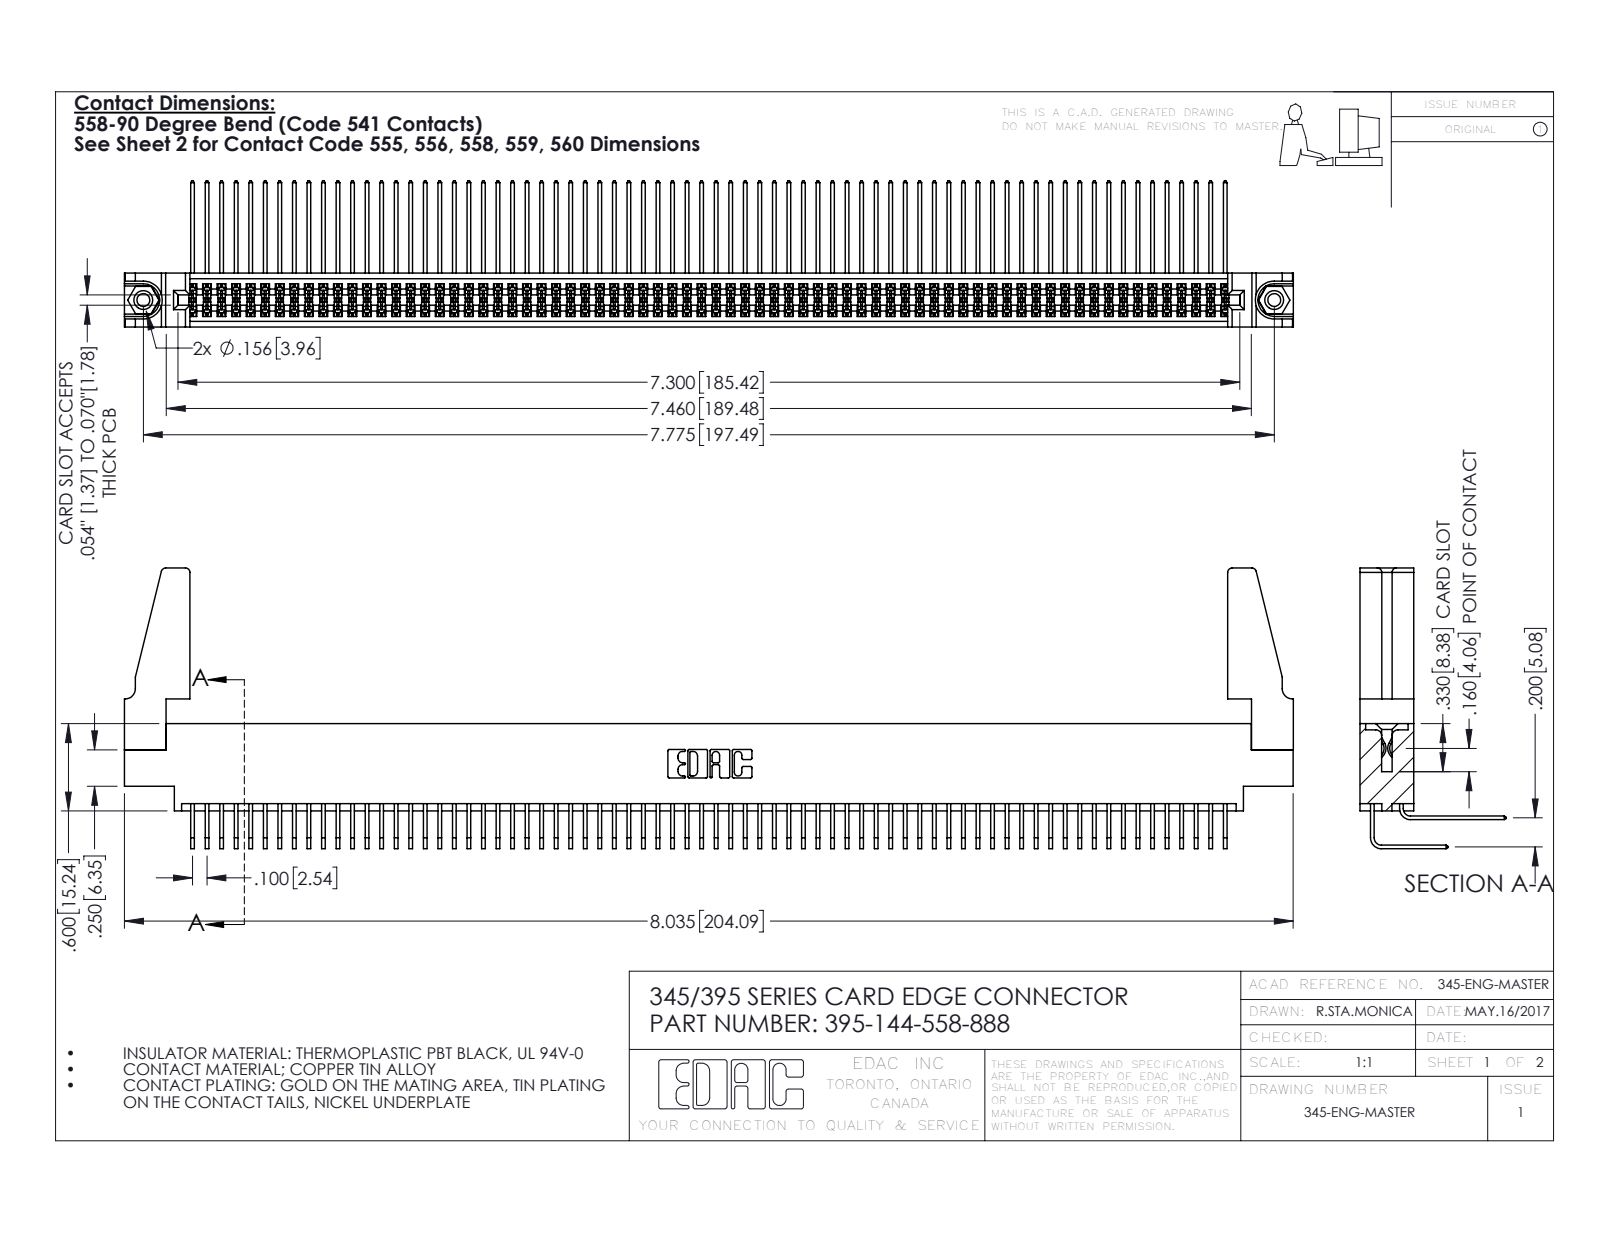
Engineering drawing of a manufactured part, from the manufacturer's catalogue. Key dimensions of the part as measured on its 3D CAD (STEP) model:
Part name (STEP PRODUCT): 345-220-078_345-220-088; 395-144-558-888; 345-292-001_558 Tail - 2; 345 Part_0.170 Offset - 0.156 Dia-TH (+2 more)
STEP written by: SolidWorks 2016 (CONFIG_CONTROL_DESIGN)
Units: inches
Bodies: 149 solids, 7742 faces (5196 planar, 2530 cylindrical, 16 other)
Overall size (bounding box): 8.036 × 1.929 × 1.005
Volume: 1.469 in³ · Surface area: 59.73 in²
Round holes (diameter × count): ⌀0.089 ×2, ⌀0.125 ×2, ⌀0.156 ×2, ⌀0.064 ×1
Round bosses / shafts (diameter × count): ⌀0.155 ×2
Partial cylindrical surfaces — rounded edges, fillets, slot ends (radius × count): R0.006 ×216, R0.01 ×22, R0.03 ×8, R0.007 ×6, R0.031 ×6, R0.026 ×3, R0.014 ×2, R0.019 ×2
Main face-to-face distances: 0.072, 0.298, 0.2, 0.37, 0.098, 0.272, 0.025, 0.225, 0.175, 0.025
Hole centre spacings: 0.27, 7.539, 7.775
